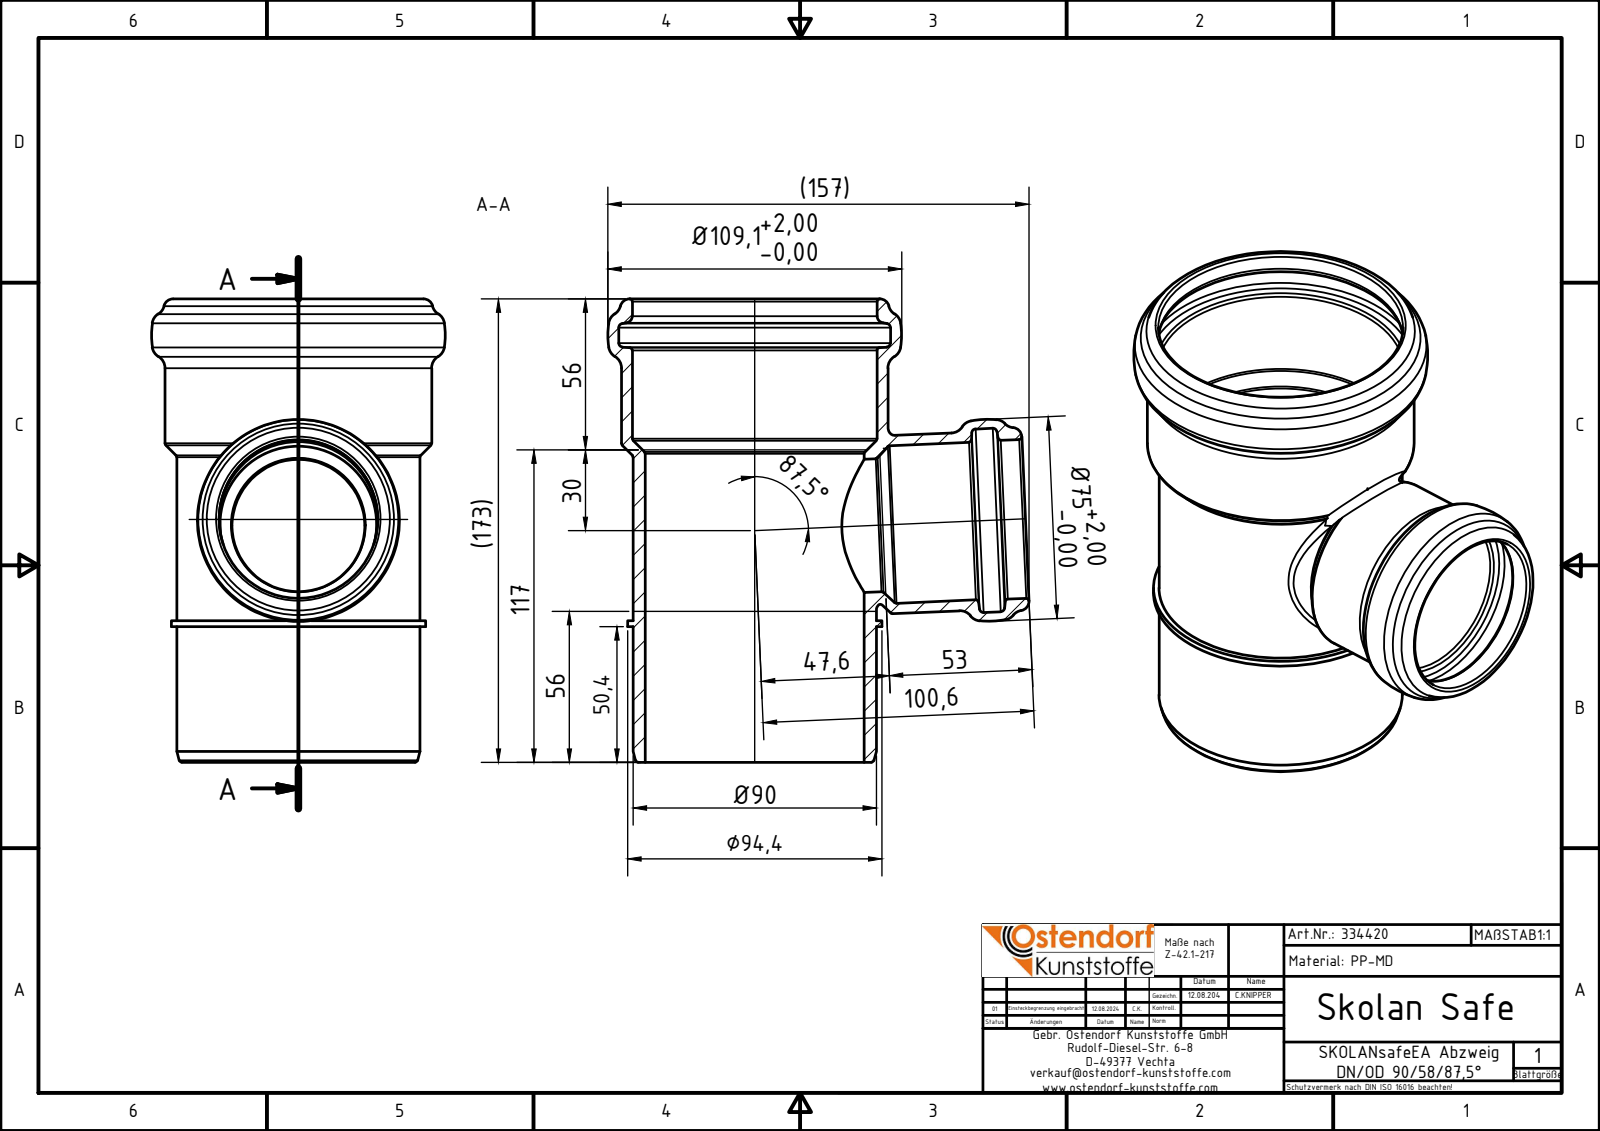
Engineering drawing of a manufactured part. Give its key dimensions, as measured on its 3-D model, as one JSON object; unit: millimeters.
{"part_name": "334420z", "step_written_by": "Autodesk Inventor 2024 (AUTOMOTIVE_DESIGN)", "units": "millimeters", "bodies": {"solids": 1, "faces": 63, "planar": 4, "cylindrical": 15, "other": 44}, "overall_size": [172, 156.39, 109.1], "volume_mm3": 264497, "surface_area_mm2": 125880, "round_holes": [[49.4, 1], [58.5, 1], [59, 1], [68.2, 1], [81.3, 1], [90.8, 1], [90.9, 1], [100.9, 1]], "round_bosses_or_shafts": [[99, 1], [94.4, 1], [90.3, 1], [66.1, 1]], "partial_cylinders_radius": [[29, 1]], "face_to_face_distances": [52.6, 50.4, 2.2]}
